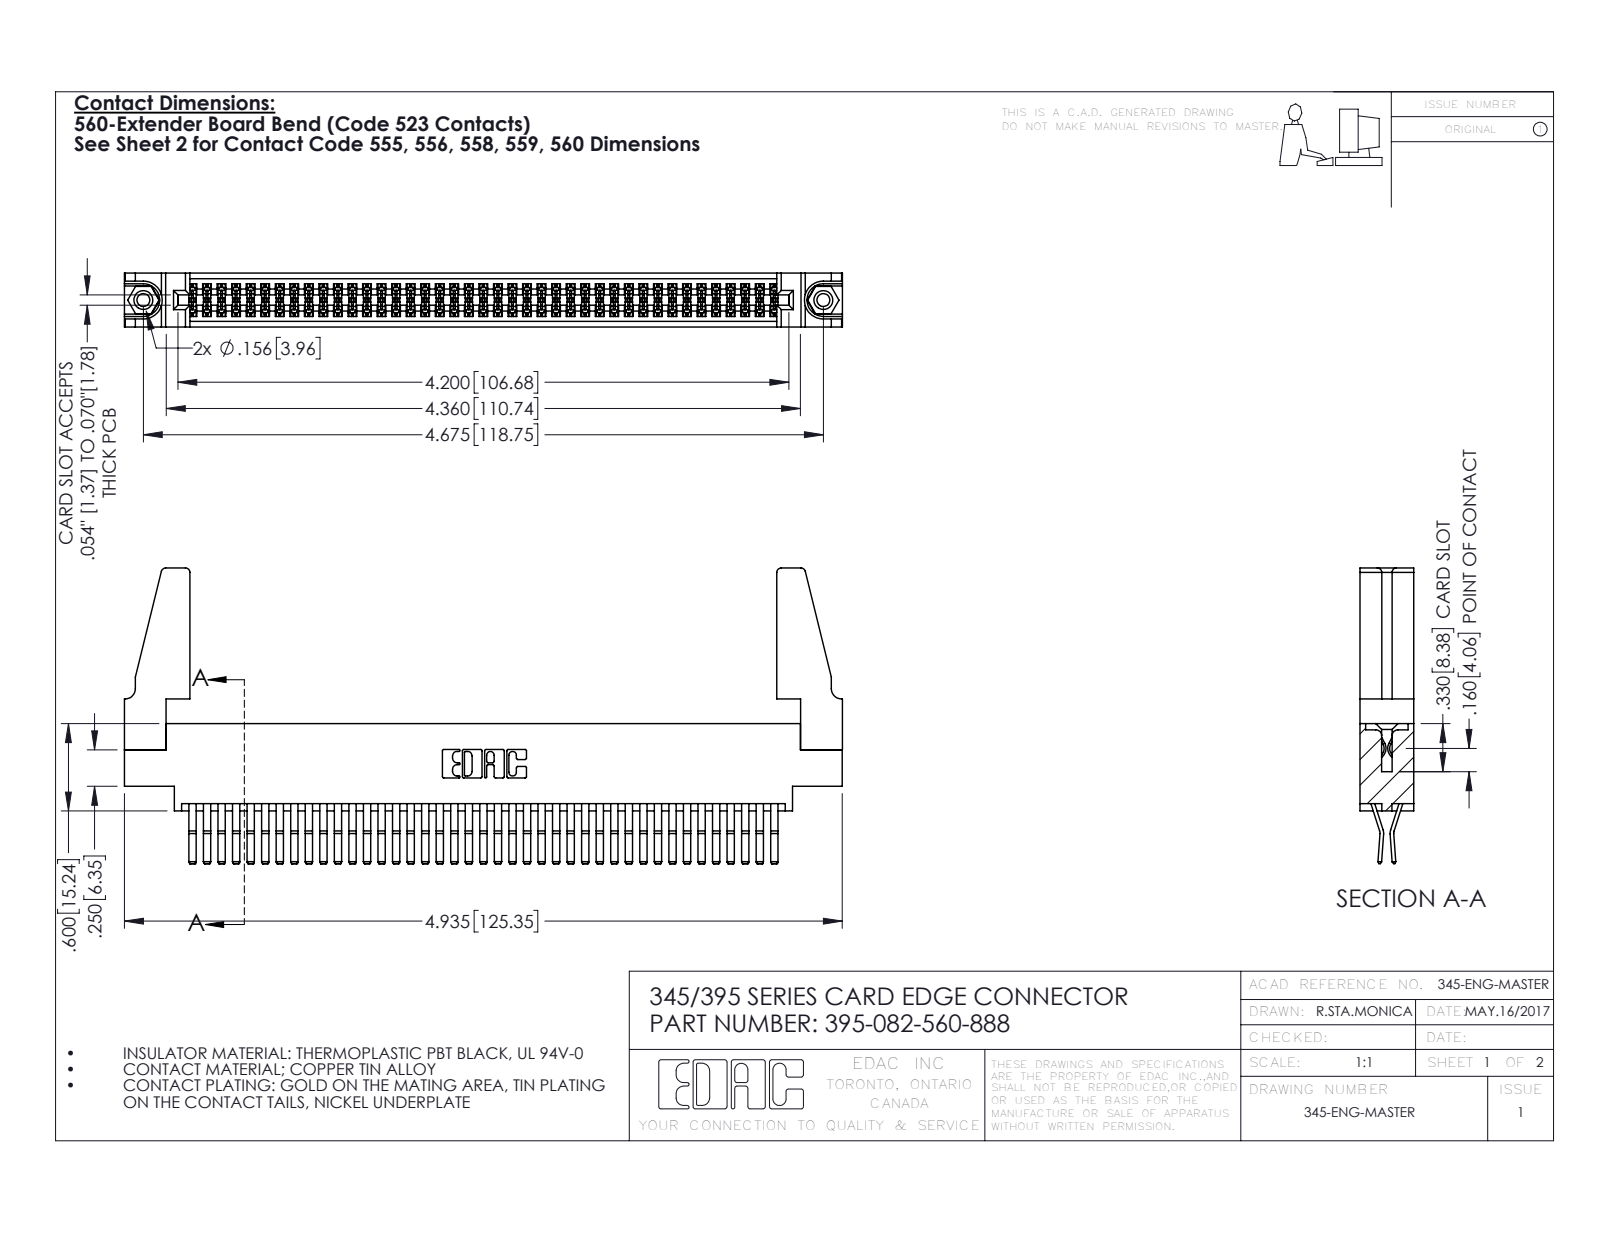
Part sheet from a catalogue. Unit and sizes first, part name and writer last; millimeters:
Units: millimetres
Overall size (bounding box): 125.4 × 51.6 × 9.4
Round holes (diameter × count): ⌀2.3 ×2, ⌀3.2 ×2, ⌀4 ×2, ⌀1.6 ×1
Round bosses / shafts (diameter × count): ⌀3.9 ×2
Partial cylindrical surfaces — rounded edges, fillets, slot ends (radius × count): R0.2 ×124, R0.3 ×22, R0.8 ×8, R0.2 ×6, R0.8 ×6, R0.7 ×3, R0.3 ×2, R0.4 ×2
Main face-to-face distances: 1.8, 7.6, 0.6, 9.4, 5.1, 2.5, 6.9, 5.7, 4.4, 3.8
Hole centre spacings: 6.9, 112.8, 118.7
Volume: 15 800 mm³ · Surface area: 23 250 mm²
Bodies: 87 solids, 4518 faces (2862 planar, 1640 cylindrical, 16 other)
Part name (STEP PRODUCT): 345-292-001_560 Tail; 345-220-078_345-220-088; 345 Part_0.170 Offset - 0.156 Dia-TH; 345-250-001_345-250-001-102 (+1 more)
STEP written by: SolidWorks 2016 (CONFIG_CONTROL_DESIGN)
